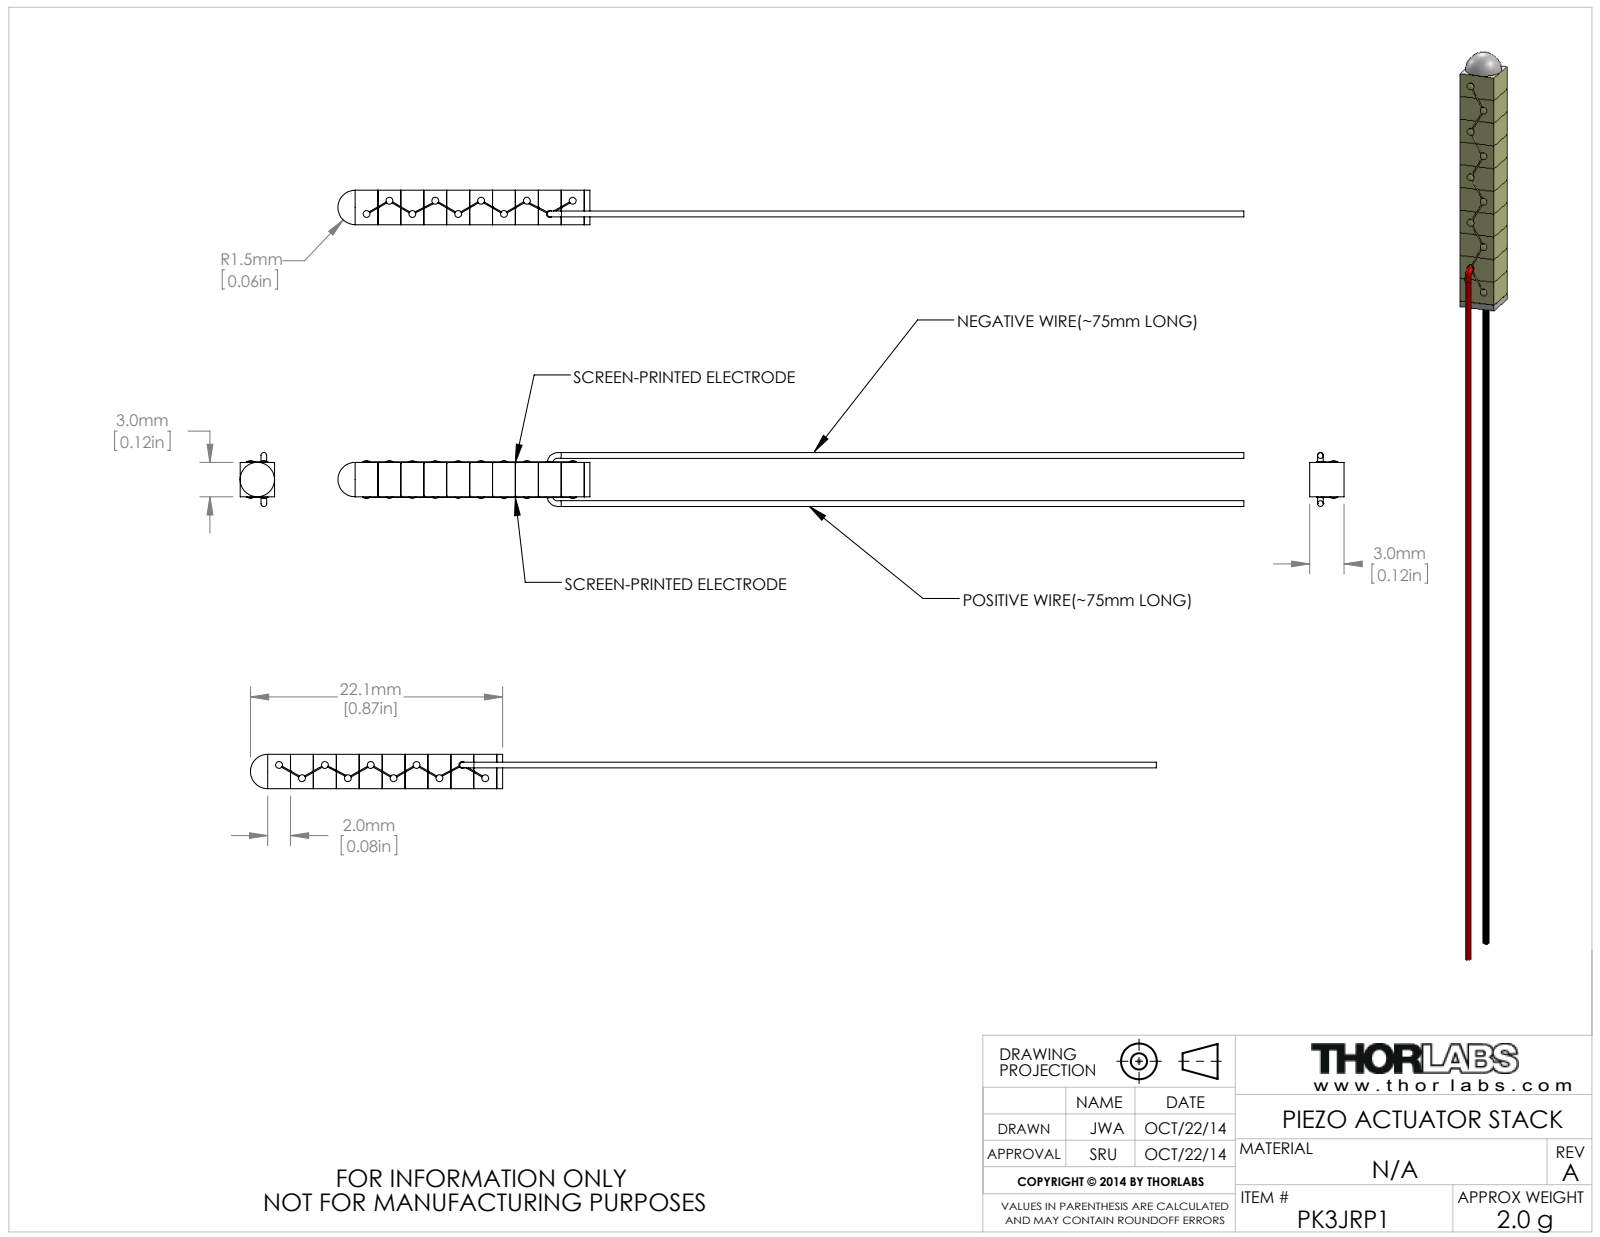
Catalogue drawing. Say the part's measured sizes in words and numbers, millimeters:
The part is named "PK3JRP1". Its 3-D file was written by "SolidWorks 2012 (AUTOMOTIVE_DESIGN)". It is 5 solids with 236 faces: 97 planar, 96 cylindrical and 43 other. Overall it measures 79.1 by 4.72 by 3 millimeters. Its volume is 216 cubic millimeters and its surface area 654 square millimeters. Round bosses or shafts: 10 of diameter 0.6. The main face-to-face distances are 2, 4, 3, 6, 8, 10, 12, 14, 16, 18.
